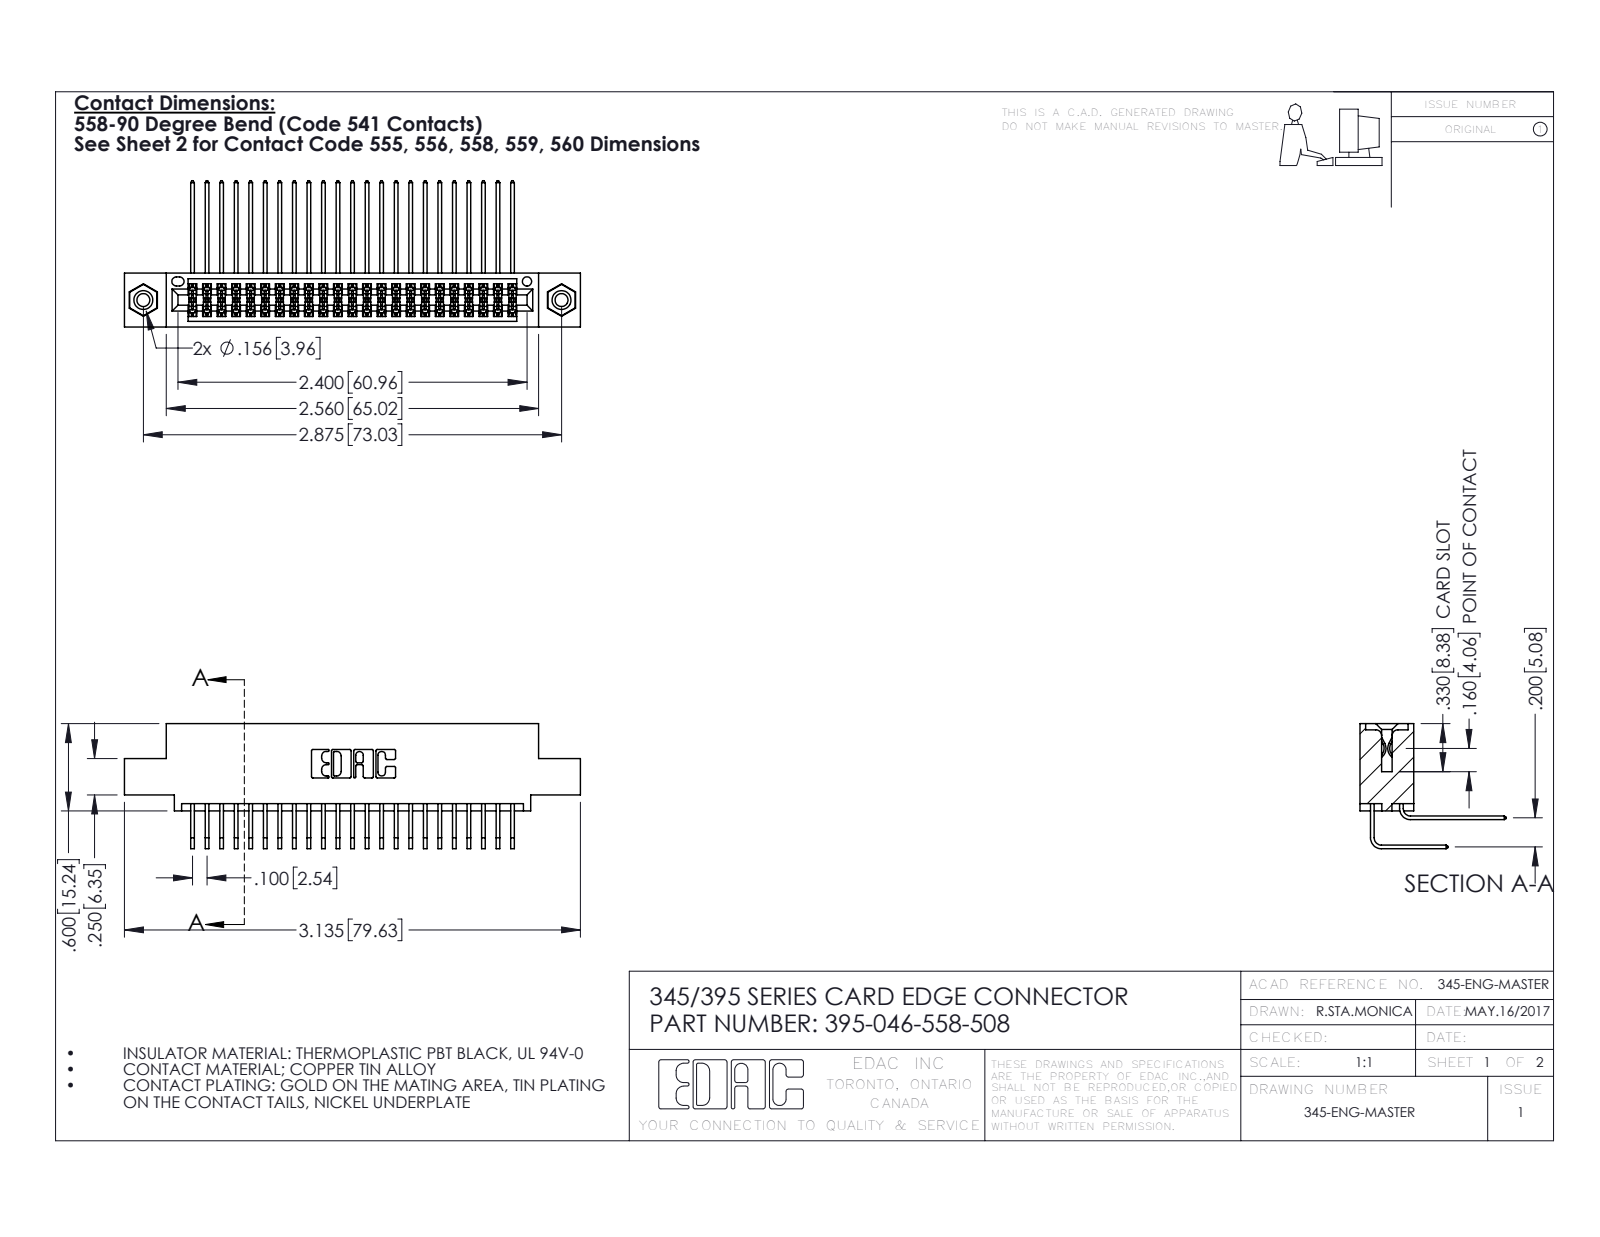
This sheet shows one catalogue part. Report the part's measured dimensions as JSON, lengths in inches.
{"part_name": "345 Part_0.110 Offset - 0.156 Dia-TI; 345-292-001_558 Tail - 2; 395-046-558-508; 345-250-001_345-250-003-102 (+1 more)", "step_written_by": "SolidWorks 2016 (CONFIG_CONTROL_DESIGN)", "units": "inches", "bodies": {"solids": 49, "faces": 2582, "planar": 1726, "cylindrical": 840, "other": 16}, "overall_size": [3.135, 1.005, 0.859], "volume_in3": 0.473, "surface_area_in2": 19.27, "round_holes": [[0.089, 2], [0.125, 2], [0.156, 2], [0.064, 1]], "round_bosses_or_shafts": [[0.155, 2]], "partial_cylinders_radius": [[0.006, 70], [0.01, 22], [0.007, 6], [0.031, 6], [0.026, 3], [0.014, 2], [0.019, 2], [0.022, 2]], "face_to_face_distances": [0.2, 0.072, 0.298, 0.37, 0.098, 0.272, 0.025, 0.225, 0.025, 0.175], "hole_center_spacings": [0.27, 2.641, 2.875]}
